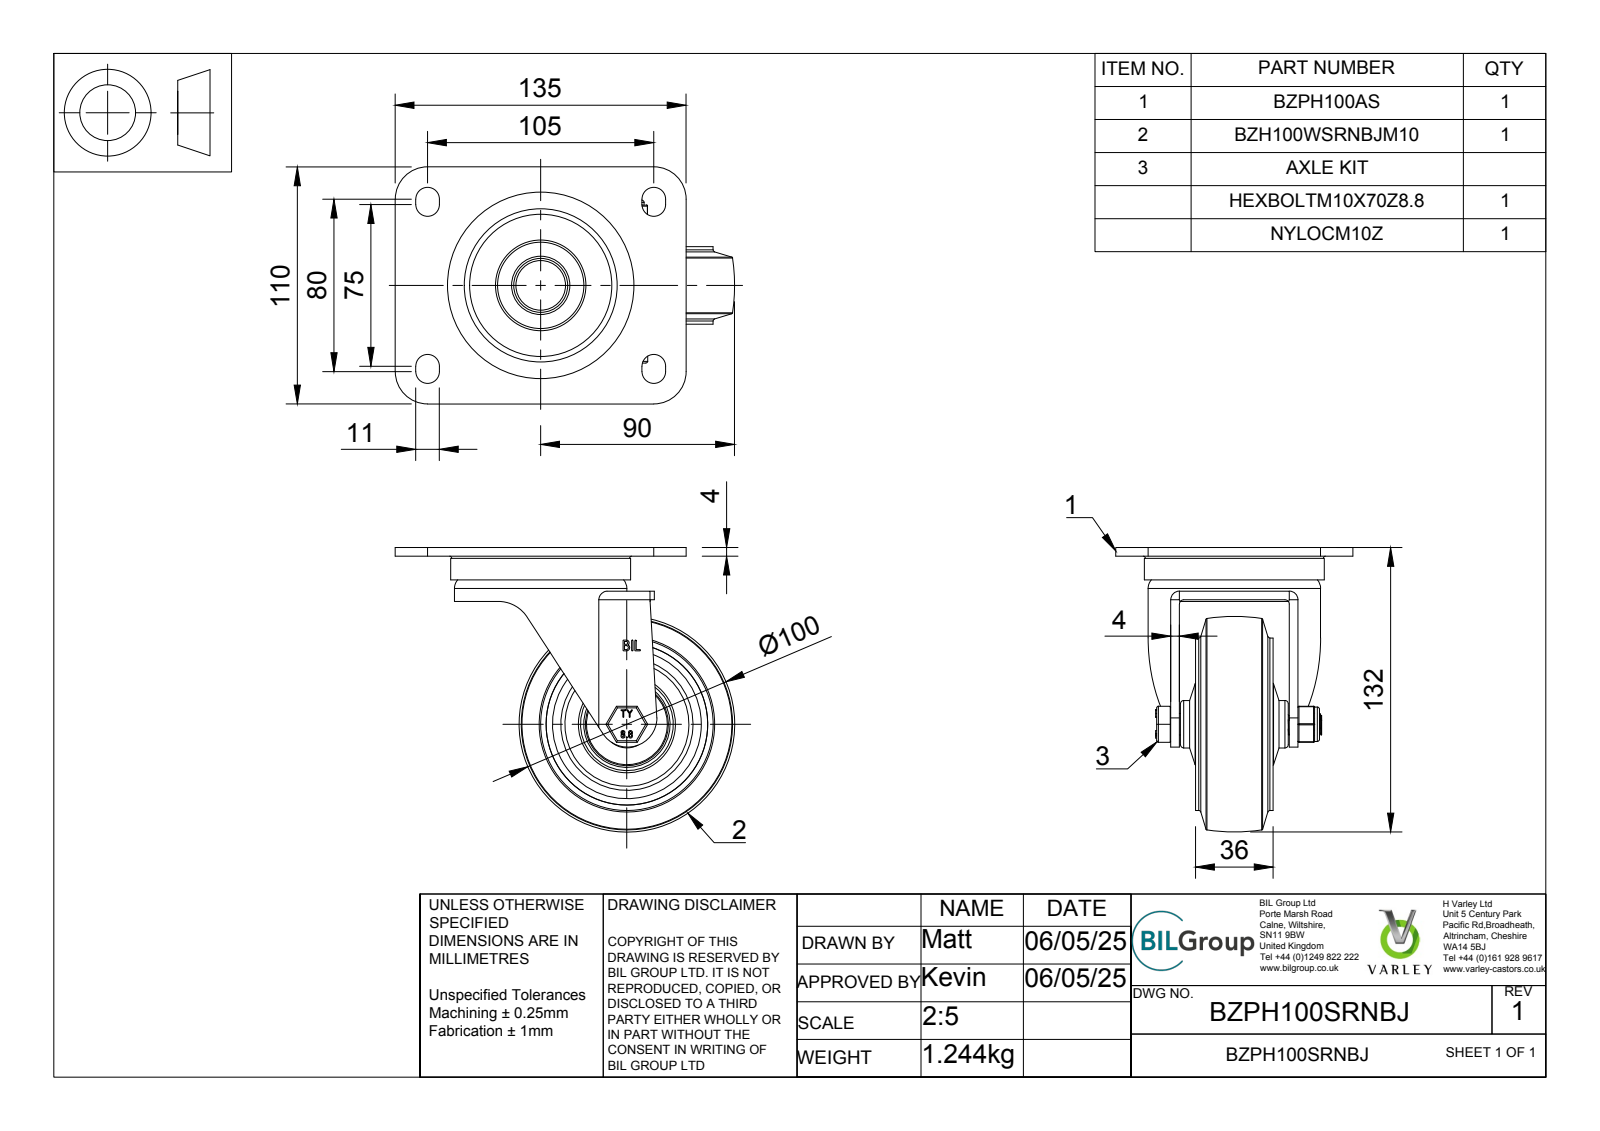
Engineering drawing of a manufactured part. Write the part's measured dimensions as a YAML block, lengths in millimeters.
part_name: "BZPH100SRNBJ v3; BZPH100AS v1; ZINC PLATED, PRESSED STEEL TOP PLATE; ZINC PLATED, PRESSED STEEL FORKS (+8 more)"
step_written_by: "Autodesk Translation Framework v14.4.0.0 (AUTOMOTIVE_DESIGN)"
units: millimeters
bodies: {solids: 24, faces: 780, planar: 331, cylindrical: 177, other: 272}
overall_size: [157.5, 132, 110]
volume: 335647
surface_area: 154517
round_holes:
  - {diameter: 26, count: 2}
  - {diameter: 10, count: 1}
  - {diameter: 10.2, count: 1}
  - {diameter: 12, count: 1}
  - {diameter: 15, count: 1}
  - {diameter: 20, count: 1}
  - {diameter: 22.5, count: 1}
  - {diameter: 28, count: 1}
  - {diameter: 30, count: 1}
  - {diameter: 31, count: 1}
  - {diameter: 32, count: 1}
  - {diameter: 33, count: 1}
round_bosses_or_shafts:
  - {diameter: 80, count: 2}
  - {diameter: 83.5, count: 1}
  - {diameter: 51, count: 1}
  - {diameter: 43, count: 1}
  - {diameter: 38.5, count: 1}
  - {diameter: 35, count: 1}
  - {diameter: 32, count: 1}
  - {diameter: 30.5, count: 1}
partial_cylinders:
  - {radius: 0.5, count: 18}
  - {radius: 5.5, count: 8}
  - {radius: 0.75, count: 6}
  - {radius: 2, count: 4}
  - {radius: 15, count: 4}
  - {radius: 4, count: 2}
  - {radius: 12, count: 1}
  - {radius: 13.6, count: 1}
face_to_face_distances: [4, 9, 13, 21, 11.5, 55, 17, 15, 8, 26.5]
